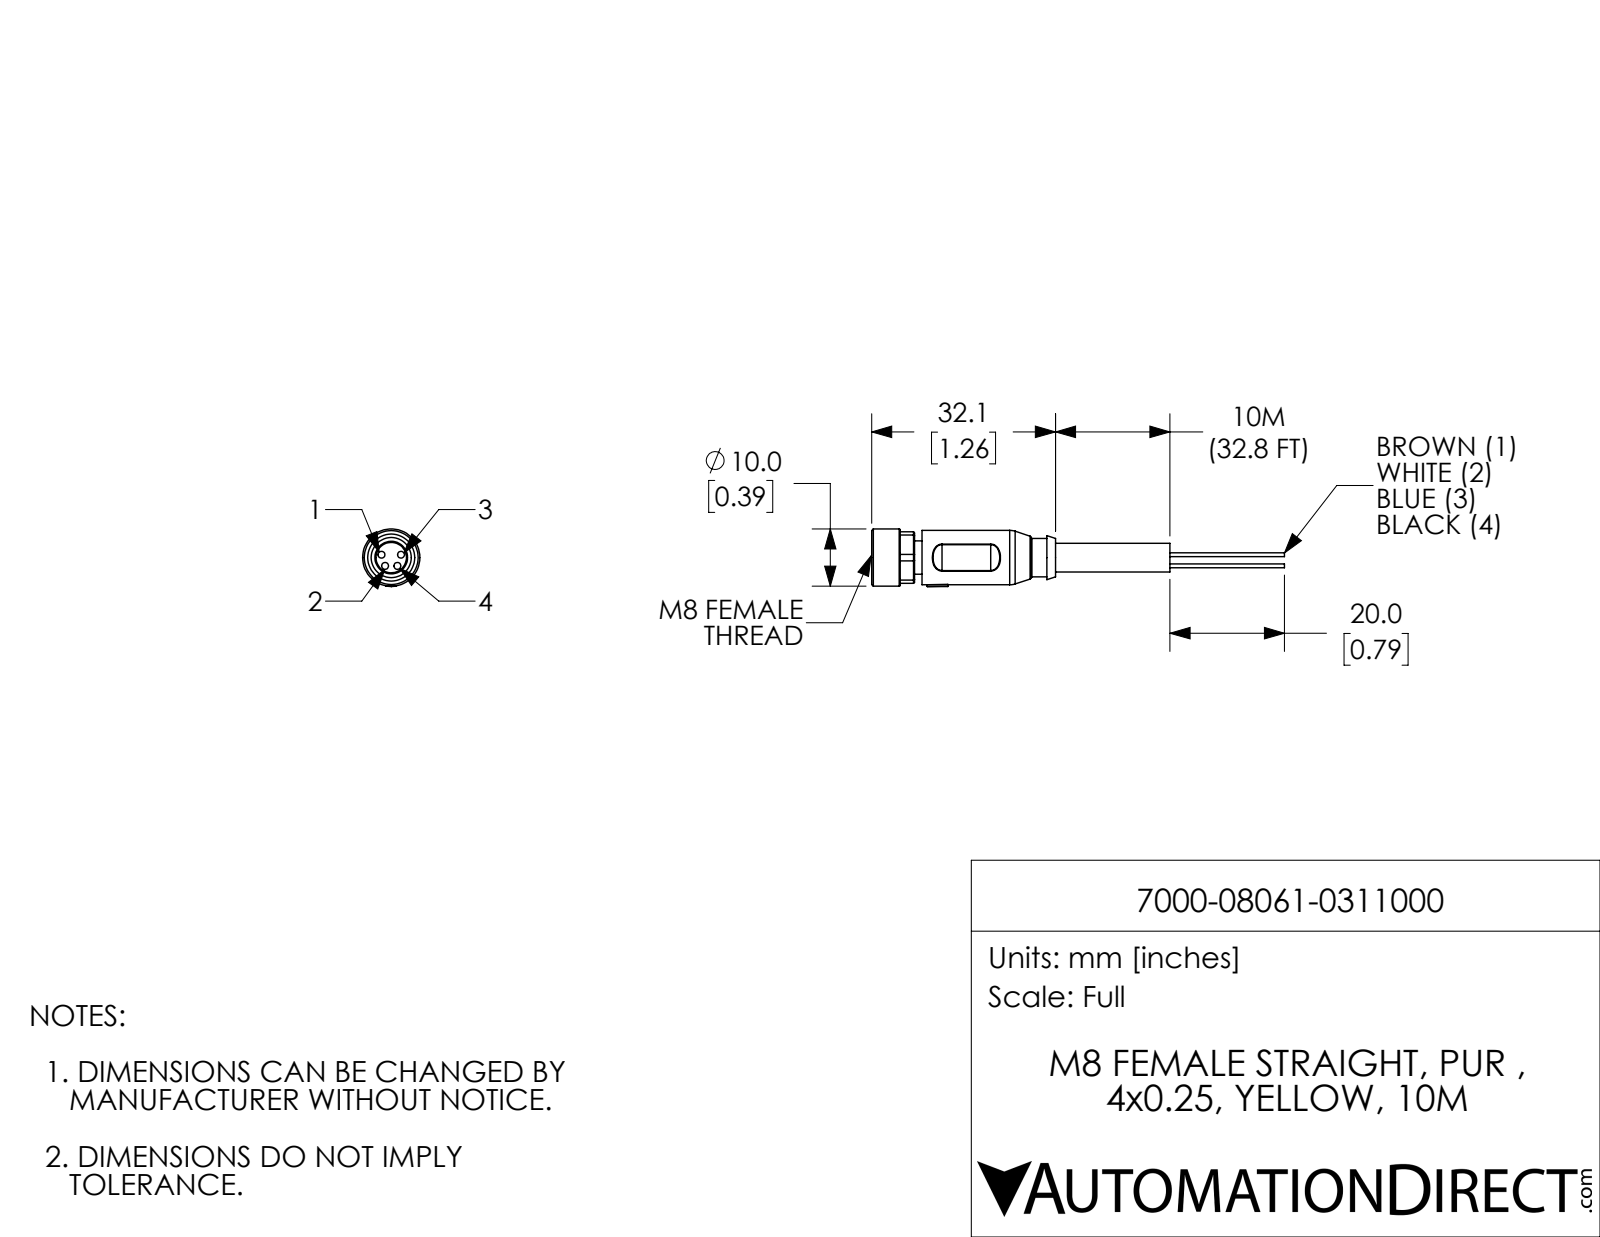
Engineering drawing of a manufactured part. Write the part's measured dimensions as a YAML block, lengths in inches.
part_name: "7000-08061-0311000"
step_written_by: "SolidWorks 2021 (CONFIG_CONTROL_DESIGN)"
units: inches
bodies: {solids: 1, faces: 115, planar: 38, cylindrical: 46, other: 31}
overall_size: [2.839, 0.396, 0.394]
volume: 0.141
surface_area: 2.944
round_holes:
  - {diameter: 0.047, count: 4}
  - {diameter: 0.276, count: 1}
round_bosses_or_shafts:
  - {diameter: 0.026, count: 4}
  - {diameter: 0.394, count: 1}
  - {diameter: 0.374, count: 1}
  - {diameter: 0.264, count: 1}
  - {diameter: 0.228, count: 1}
  - {diameter: 0.224, count: 1}
  - {diameter: 0.197, count: 1}
partial_cylinders:
  - {radius: 0.008, count: 4}
  - {radius: 0.098, count: 4}
  - {radius: 0.193, count: 1}
  - {radius: 0.199, count: 1}
face_to_face_distances: [0.327, 0.051, 0.969, 0.354, 0.059, 0.028, 1.756, 1.705, 0.268, 0.319]
hole_center_spacings: [0.07, 0.071, 0.081, 0.133, 0.084, 0.134]
